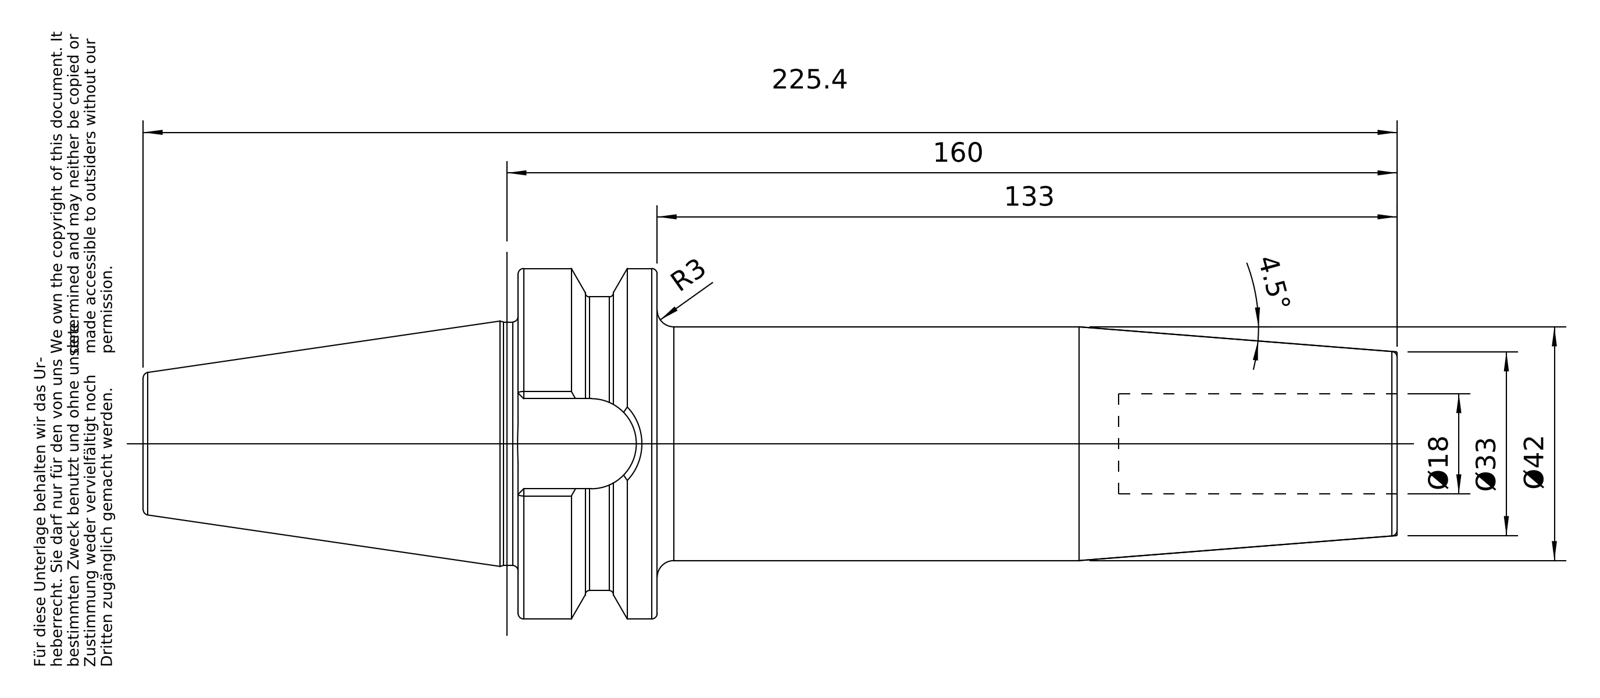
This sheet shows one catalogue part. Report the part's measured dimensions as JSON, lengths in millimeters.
{"part_name": "40-642-18", "step_written_by": "PRO/ENGINEER BY PARAMETRIC TECHNOLOGY CORPORATION, 2010430 (CONFIG_CONTROL_DESIGN)", "units": "millimeters", "bodies": {"solids": 1, "faces": 96, "planar": 26, "cylindrical": 22, "other": 48}, "overall_size": [225.4, 62.98, 62.98], "volume_mm3": 282165, "surface_area_mm2": 40689, "round_holes": [[13.84, 1], [17.01, 1], [17.5, 1], [18, 1]], "round_bosses_or_shafts": [[62.98, 1], [52.75, 1], [43.75, 1], [42, 1], [16.01, 1]], "partial_cylinders_radius": [[8.1, 1]], "face_to_face_distances": [25, 158, 133, 44.9, 108, 83, 50, 16.2, 67.4, 92.4]}
